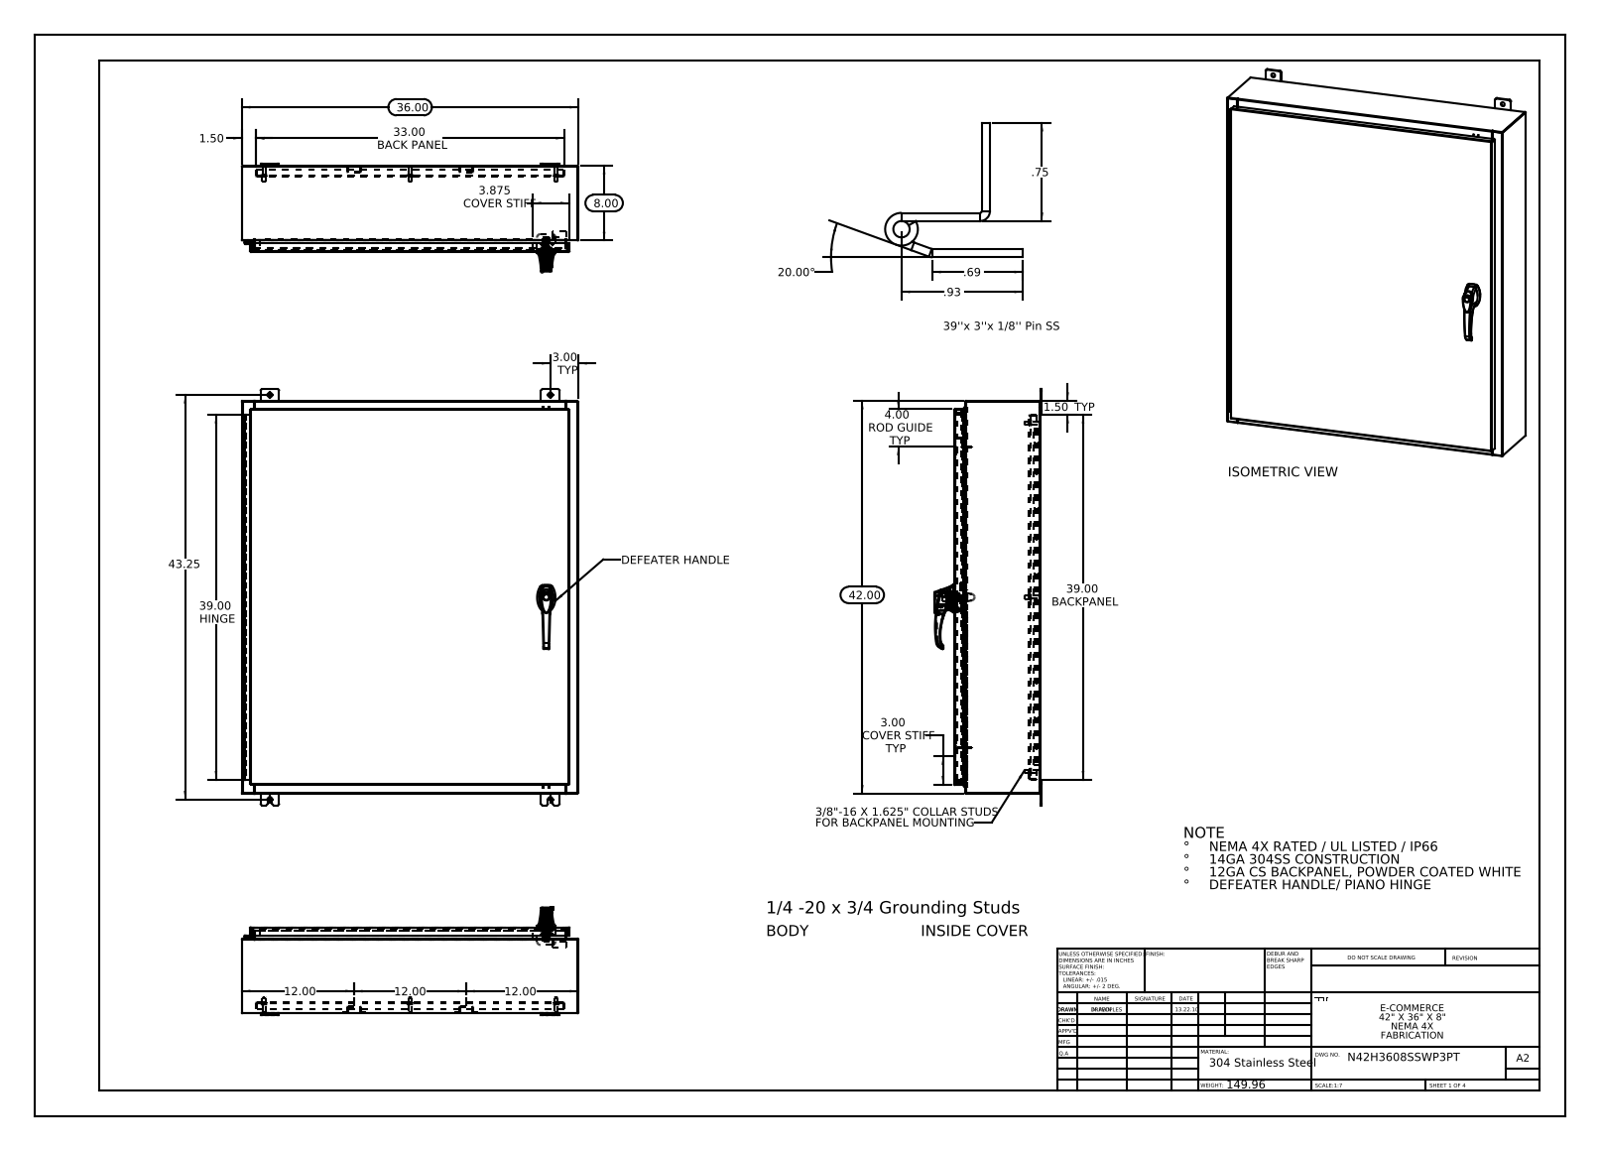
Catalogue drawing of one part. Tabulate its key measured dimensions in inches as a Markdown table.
| quantity | value |
| --- | --- |
| part name | N42H3608SSWP3PT 263033_Industrilas; 033060_032151; N42H3608SSWP3PT Body; 00005310_26163101 (+8 more) |
| STEP written by | SolidWorks 2013 (CONFIG_CONTROL_DESIGN) |
| units | inches |
| bodies | 39 solids, 3080 faces (1201 planar, 1185 cylindrical, 694 other) |
| overall size | 44.5 × 36 × 11.495 |
| volume | 538.4 in³ |
| surface area | 13 302 in² |
| round holes (diameter × count) | 0.5 × 12, 0.25 × 10, 0.138 × 3, 0.161 × 3, 0.079 × 2, 0.203 × 2, 0.313 × 2, 0.437 × 2, 0.125 × 1, 0.125 × 1, 0.197 × 1, 0.276 × 1 |
| round bosses / shafts (diameter × count) | 0.625 × 8, 0.375 × 8, 0.33 × 8, 1.181 × 1, 0.748 × 1, 0.68 × 1, 0.661 × 1, 0.639 × 1 |
| partial cylindrical surfaces (radius × count) | 0.118 × 37, 0.013 × 34, 0.006 × 33, 0.088 × 28, 0.19 × 24, 0.039 × 15, 0.028 × 12, 0.008 × 6 |
| main face-to-face distances | 0.075, 9.126, 9.051, 9.201, 0.104, 1, 8.126, 1.075, 8.051, 1.179 |
| hole center spacings | 14.36, 16.667, 18.625, 24.311, 36.379, 40.394, 31.25, 37.25 |
